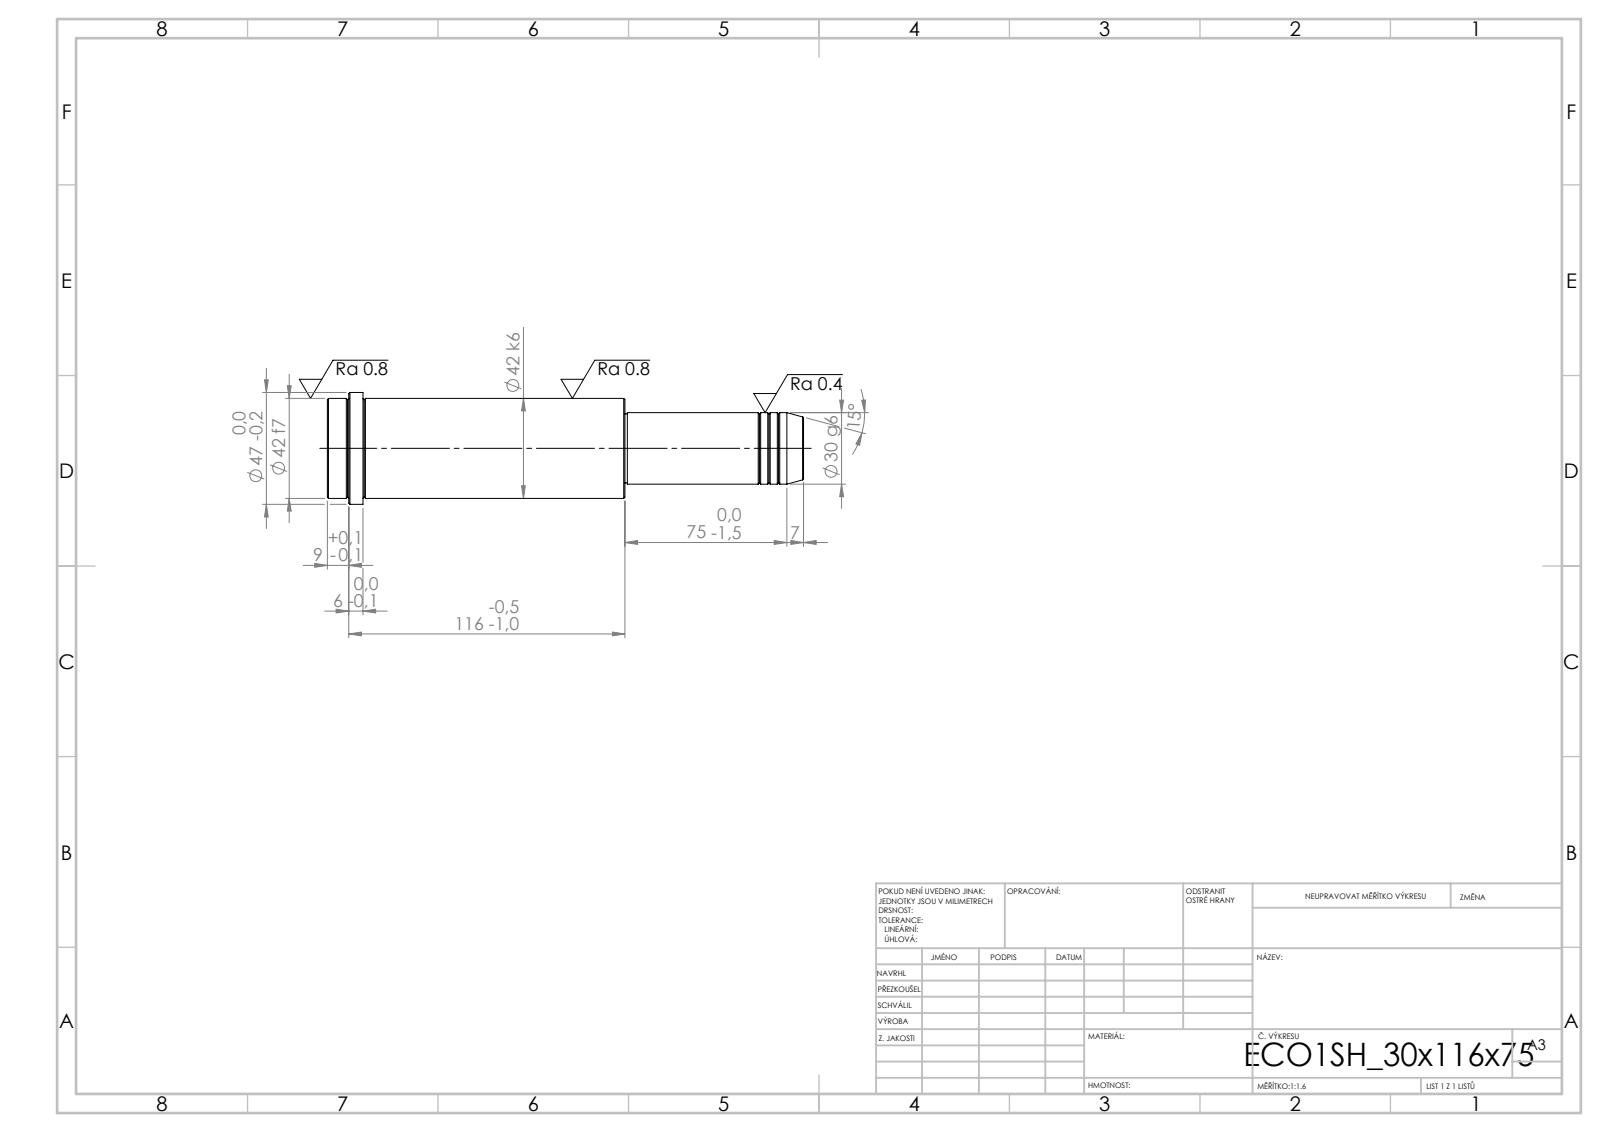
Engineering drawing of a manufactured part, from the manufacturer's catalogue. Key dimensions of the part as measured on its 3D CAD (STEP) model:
STEP written by: SolidWorks 2019 (CONFIG_CONTROL_DESIGN)
Units: millimetres
Bodies: 1 solid, 52 faces (6 planar, 16 cylindrical, 30 other)
Overall size (bounding box): 200 × 47 × 47
Volume: 227 387 mm³ · Surface area: 27 196 mm²
Round bosses / shafts (diameter × count): ⌀47 ×1, ⌀42 ×1, ⌀30 ×1, ⌀29 ×1
Main face-to-face distances: 125, 75, 200, 185, 110, 15, 191, 116, 6, 9
